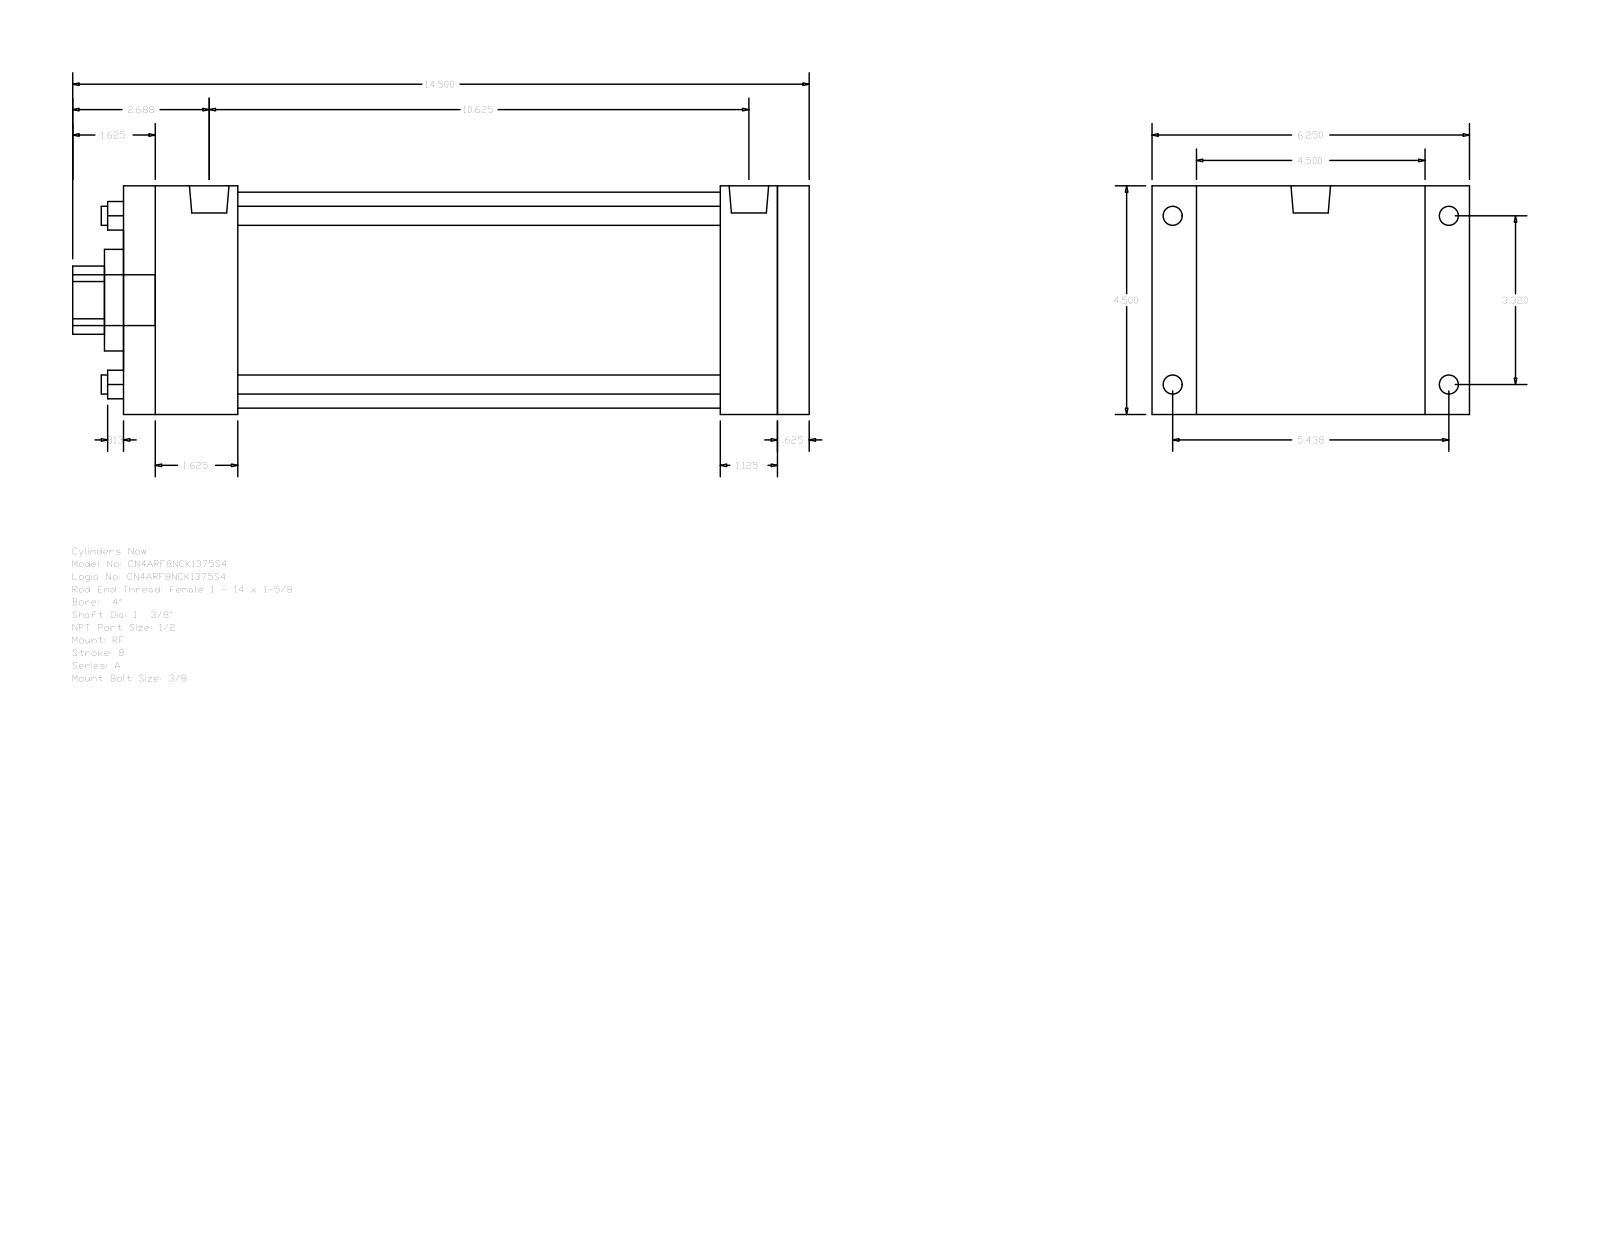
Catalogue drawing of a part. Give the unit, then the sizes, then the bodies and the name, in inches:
Units: inches
Overall size (bounding box): 14.5 × 6.25 × 4.5
Round holes (diameter × count): ⌀0.375 ×4, ⌀1.375 ×1, ⌀2 ×1, ⌀4.25 ×1
Round bosses / shafts (diameter × count): ⌀0.375 ×4, ⌀0.344 ×4, ⌀0.778 ×2, ⌀1 ×1
Partial cylindrical surfaces — rounded edges, fillets, slot ends (radius × count): R0.672 ×1
Main face-to-face distances: 4.5, 13.5, 0.625, 12.875, 1.125, 0.875, 5.375, 11.75, 1.75, 2.25
Hole centre spacings: 2.347, 3.32, 4.695
Bodies: 0 solids, 92 faces (64 planar, 28 cylindrical, 0 other)
Part name (STEP PRODUCT): A_RF__0400_1.375
STEP written by: GSSL Pune (CONFIG_CONTROL_DESIGN)
